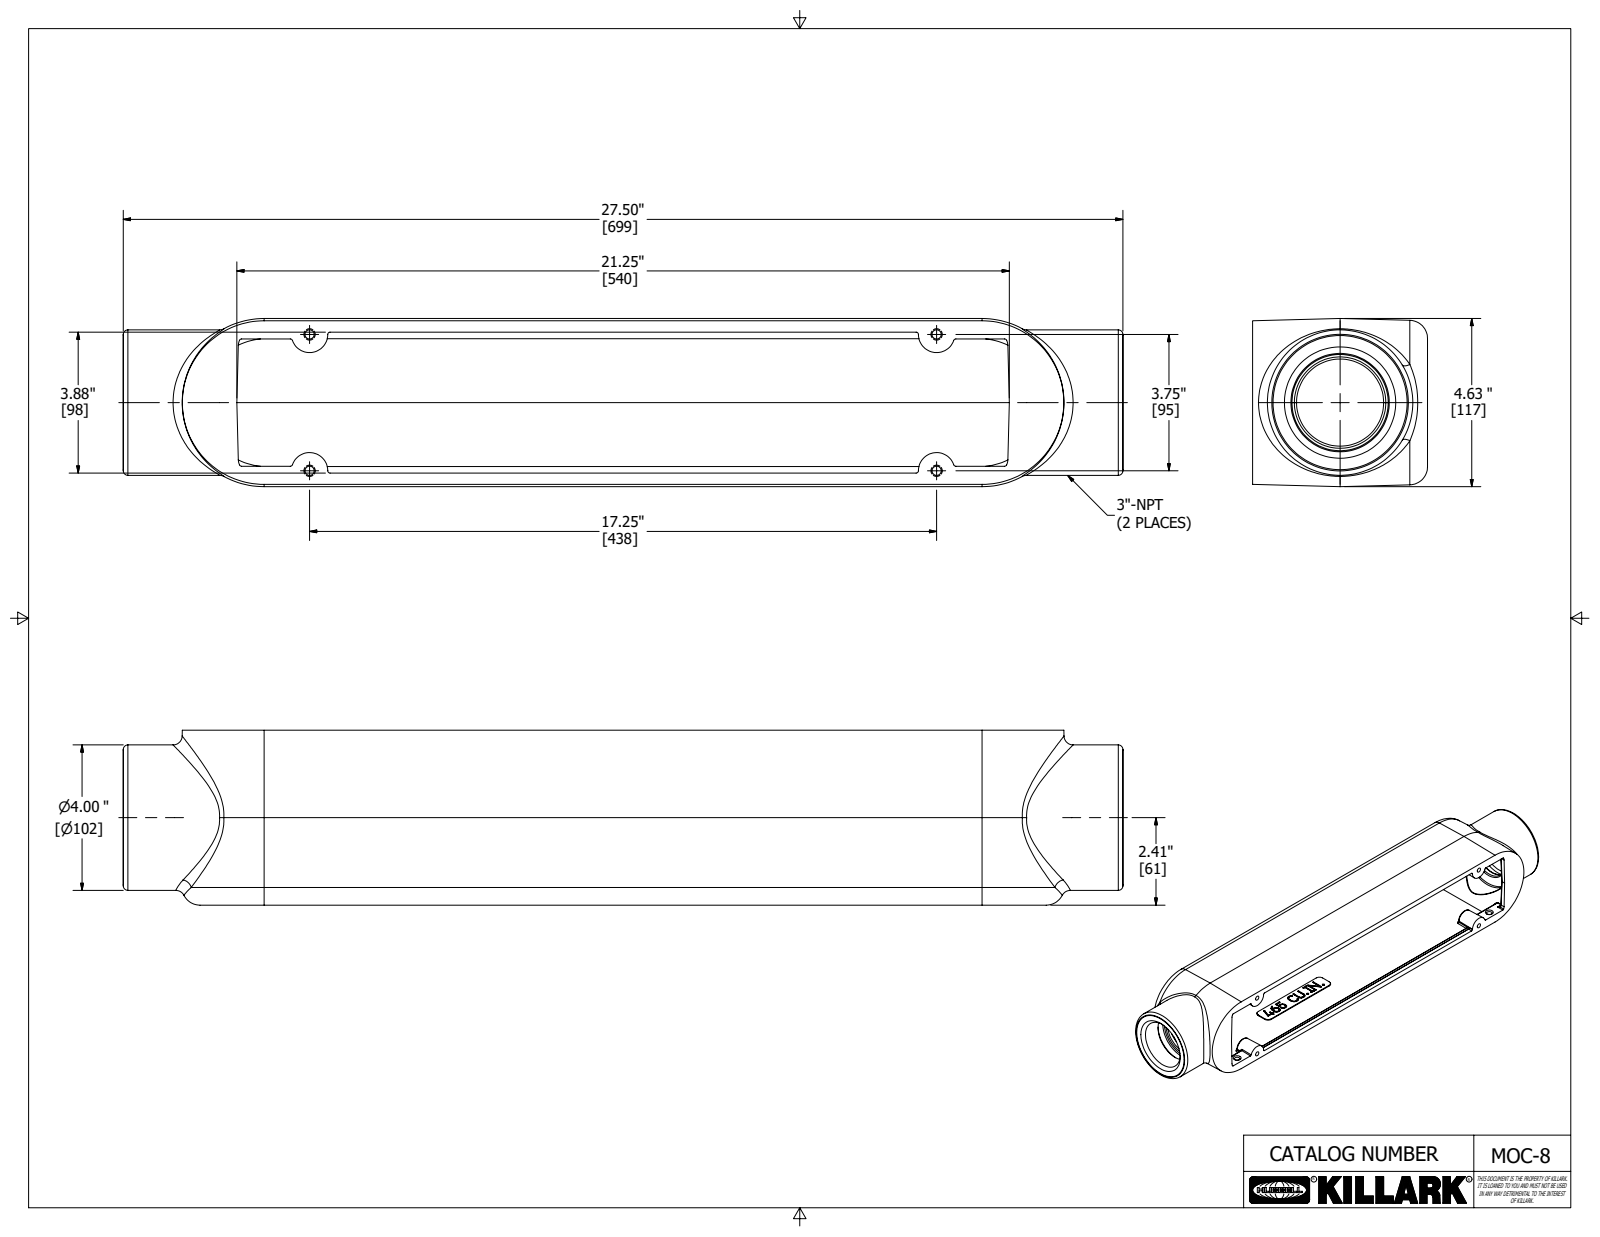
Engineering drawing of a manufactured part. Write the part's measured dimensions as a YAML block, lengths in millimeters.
part_name: "21245-2"
step_written_by: "Autodesk Inventor 2020 (AUTOMOTIVE_DESIGN)"
units: millimeters
bodies: {solids: 1, faces: 670, planar: 274, cylindrical: 92, other: 304}
overall_size: [698.5, 122.3, 117.5]
volume: 2076000
surface_area: 504100
round_holes:
  - {diameter: 6.4, count: 4}
  - {diameter: 60.9, count: 1}
  - {diameter: 73.3, count: 1}
round_bosses_or_shafts:
  - {diameter: 101.6, count: 1}
  - {diameter: 93.7, count: 1}
partial_cylinders:
  - {radius: 1.6, count: 50}
  - {radius: 9.5, count: 4}
  - {radius: 3.2, count: 2}
  - {radius: 6.3, count: 2}
  - {radius: 12.7, count: 2}
  - {radius: 50.8, count: 2}
face_to_face_distances: [117.5, 101.6, 122.3, 0.8, 121.4, 1.6, 100, 599.5, 108, 0.8]
hole_center_spacings: [95.3, 438.2, 448.4]
